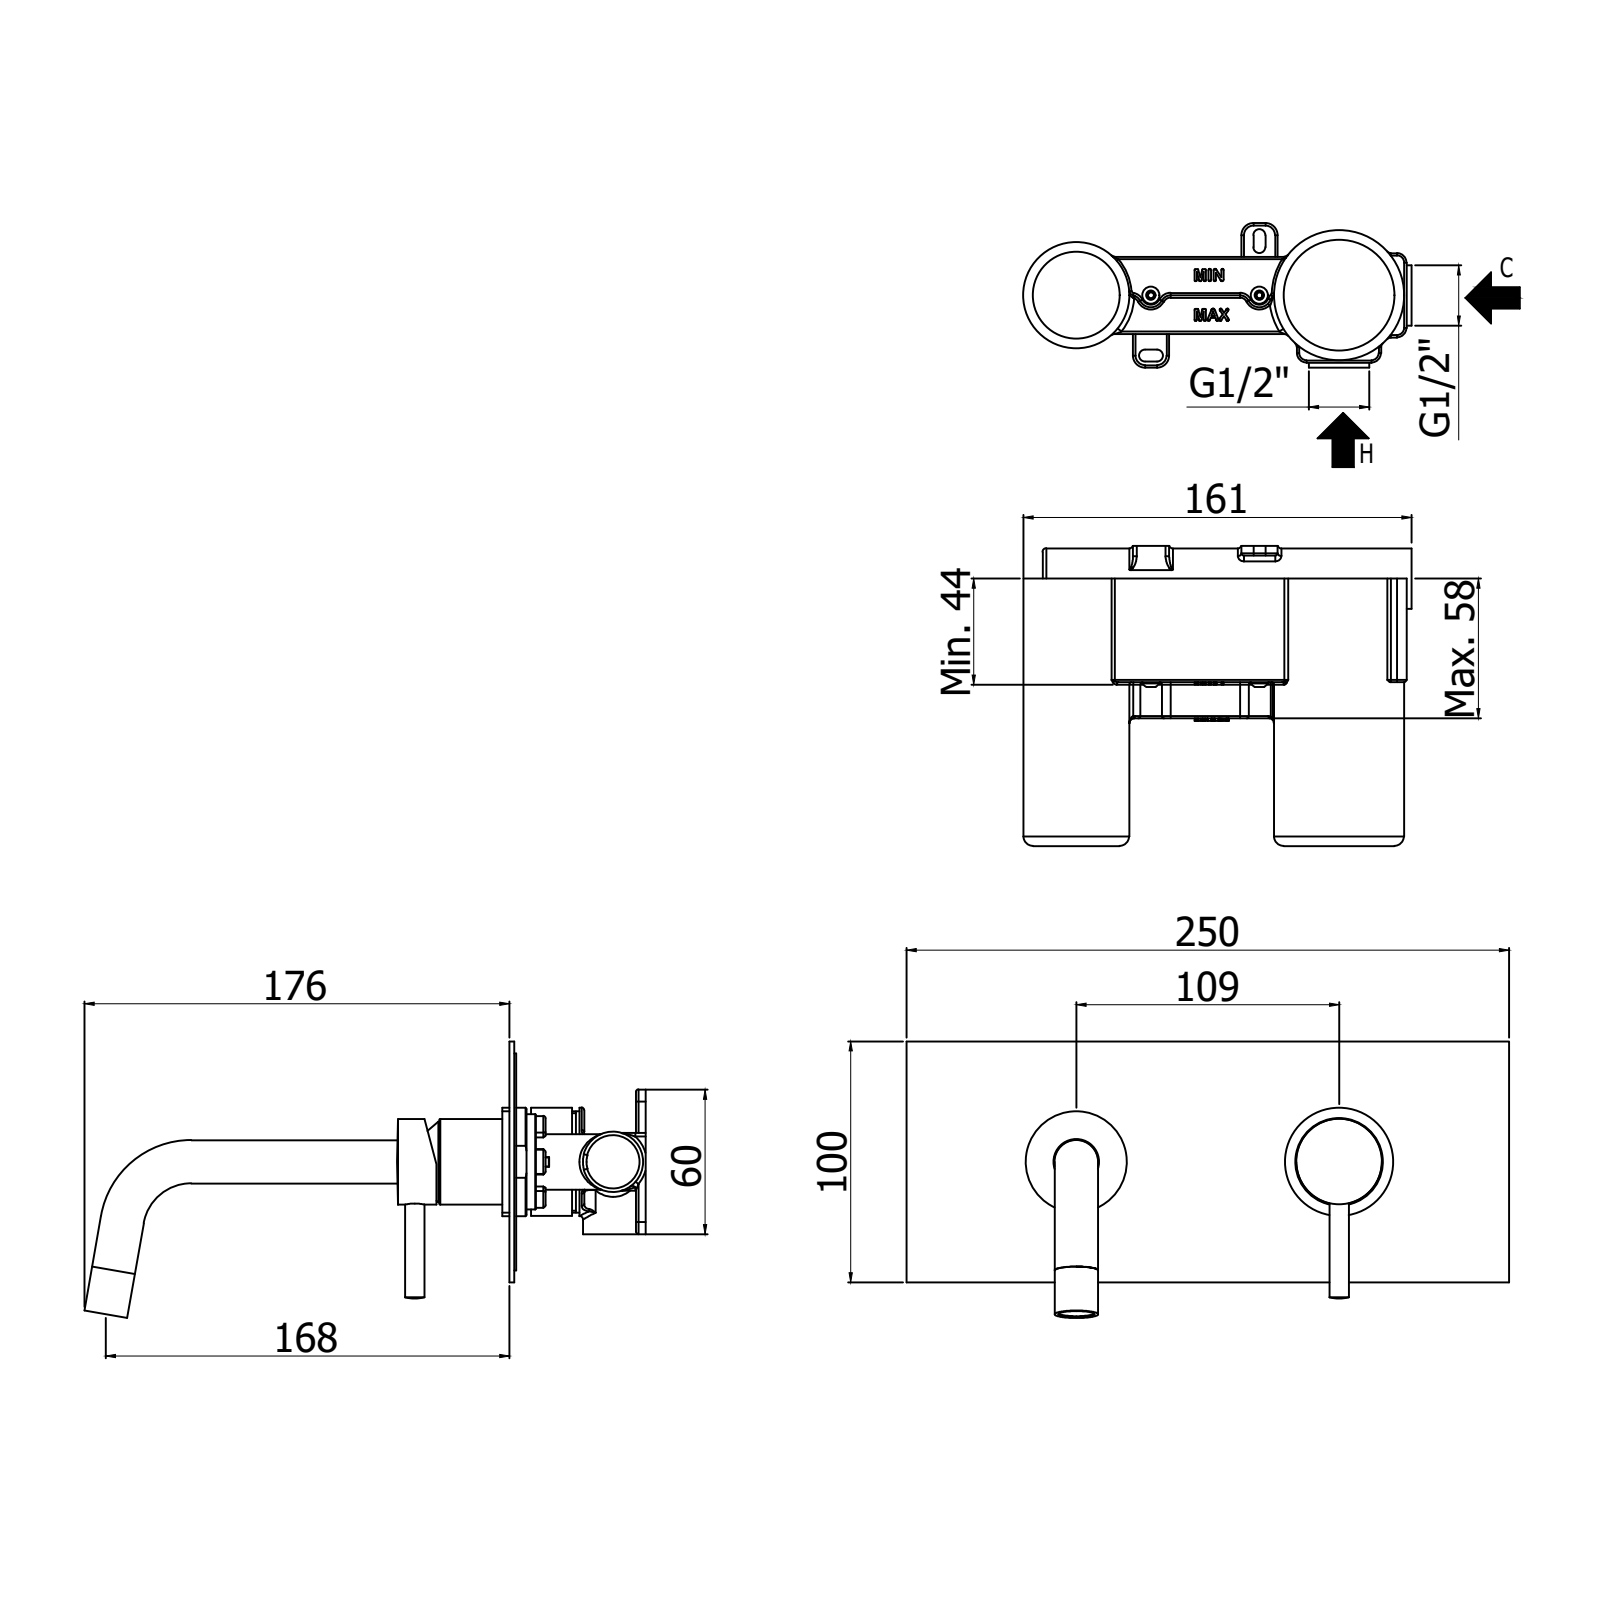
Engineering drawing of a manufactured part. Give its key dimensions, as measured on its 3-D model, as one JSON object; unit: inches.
{"part_name": "LIG101CR-M", "step_written_by": "CREO PARAMETRIC BY PTC INC, 2020044 (CONFIG_CONTROL_DESIGN)", "units": "inches", "bodies": {"solids": 0, "faces": 55, "planar": 23, "cylindrical": 20, "other": 12}, "overall_size": [9.843, 6.905, 4.519], "round_bosses_or_shafts": [[0.709, 3], [1.398, 2], [2.087, 1], [2.008, 1], [1.319, 1], [0.315, 1]], "partial_cylinders_radius": [[0.098, 1], [0.327, 1]], "face_to_face_distances": [0.079, 0.276, 0.197, 1.063, 0.984, 0.787, 3.937, 1.528, 1.449, 1.252]}
